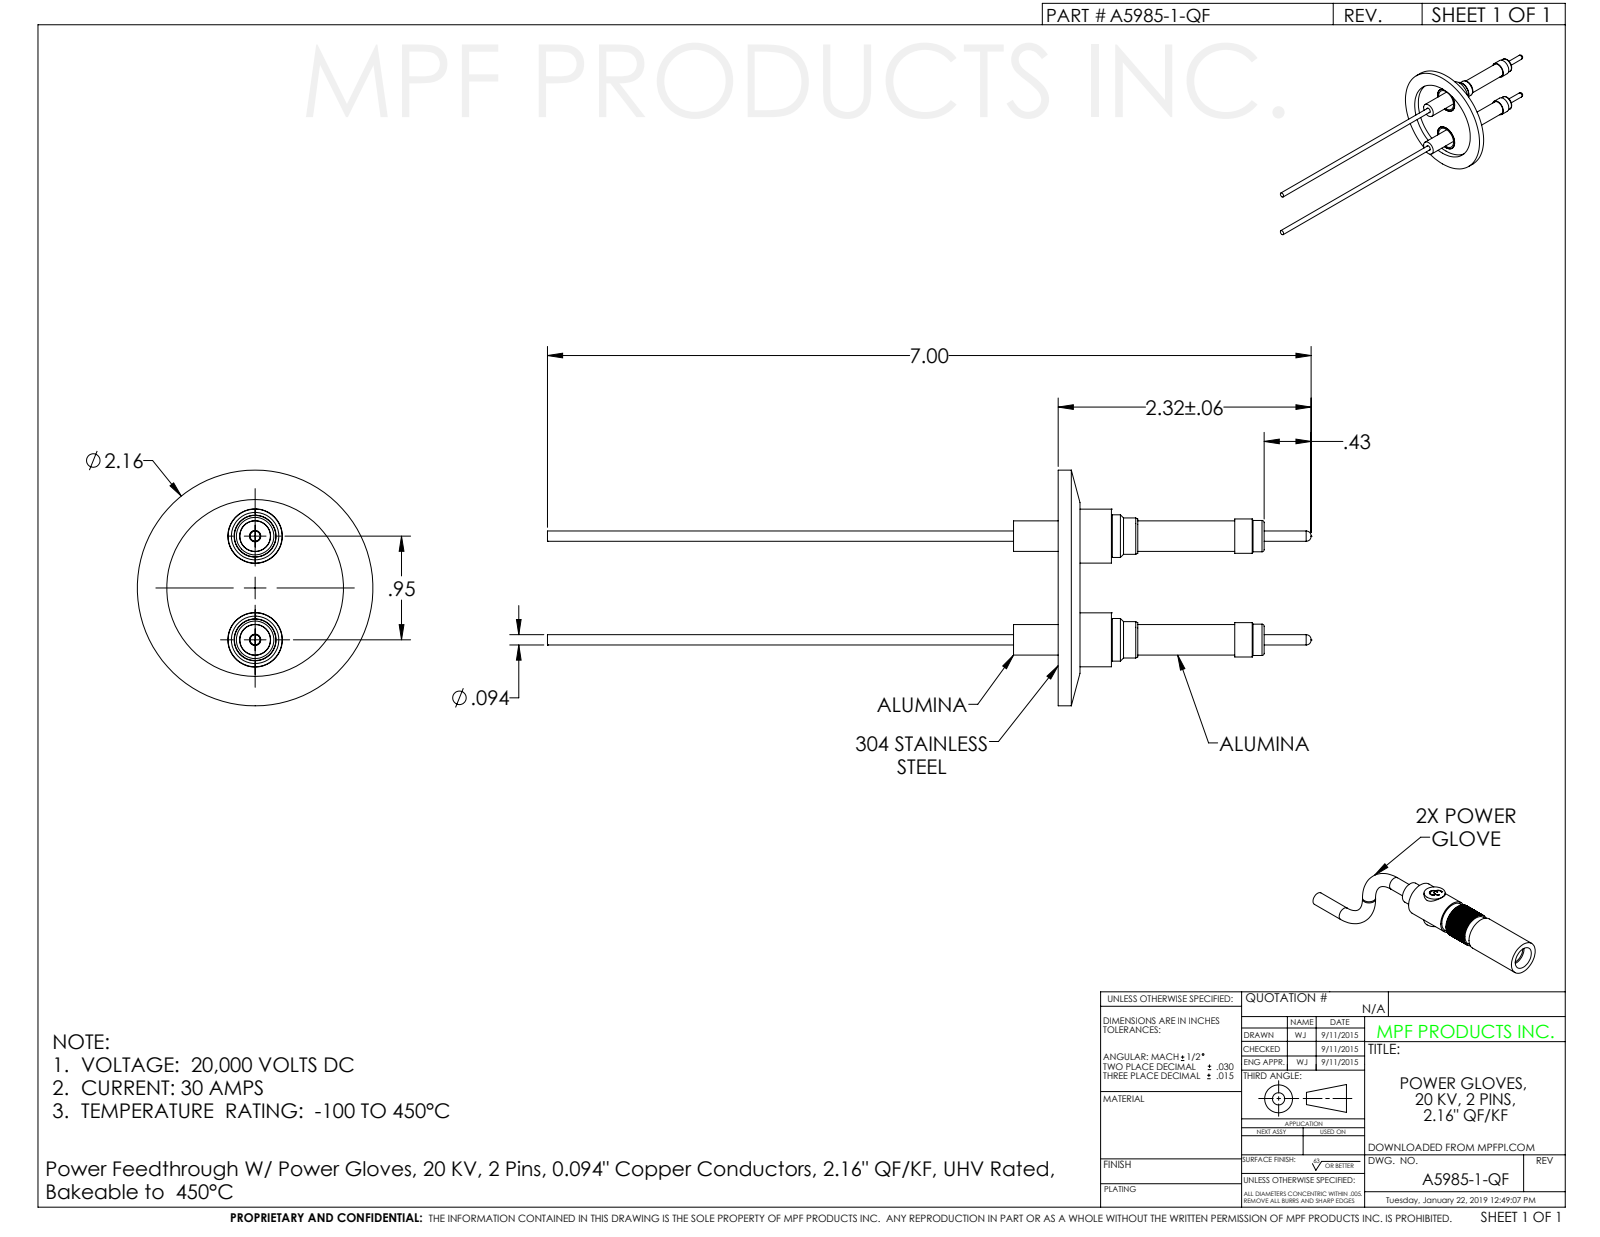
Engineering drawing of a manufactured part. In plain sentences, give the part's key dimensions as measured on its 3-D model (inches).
The part is named "A5985-1-QF". Its 3-D file was written by "SolidWorks 2012 (CONFIG_CONTROL_DESIGN)". It is 1 solid with 135 faces: 25 planar, 64 cylindrical and 46 other. Overall it measures 7 by 2.161 by 2.161 inches. Its volume is 0.796 cubic inches and its surface area 21.36 square inches. Round holes: 2 of diameter 0.105, 2 of diameter 0.259, 2 of diameter 0.344, 2 of diameter 0.385, 2 of diameter 0.435, 1 of diameter 1.63. Round bosses or shafts: 2 of diameter 0.495, 2 of diameter 0.391, 2 of diameter 0.372, 2 of diameter 0.312, 2 of diameter 0.306, 2 of diameter 0.287, 2 of diameter 0.28, 2 of diameter 0.094. The main face-to-face distances are 0.105, 0.2, 0.095, 0.488, 0.383, 0.288, 0.4, 0.505, 0.6, 0.888. The hole center spacings are 0.475, 0.95.
